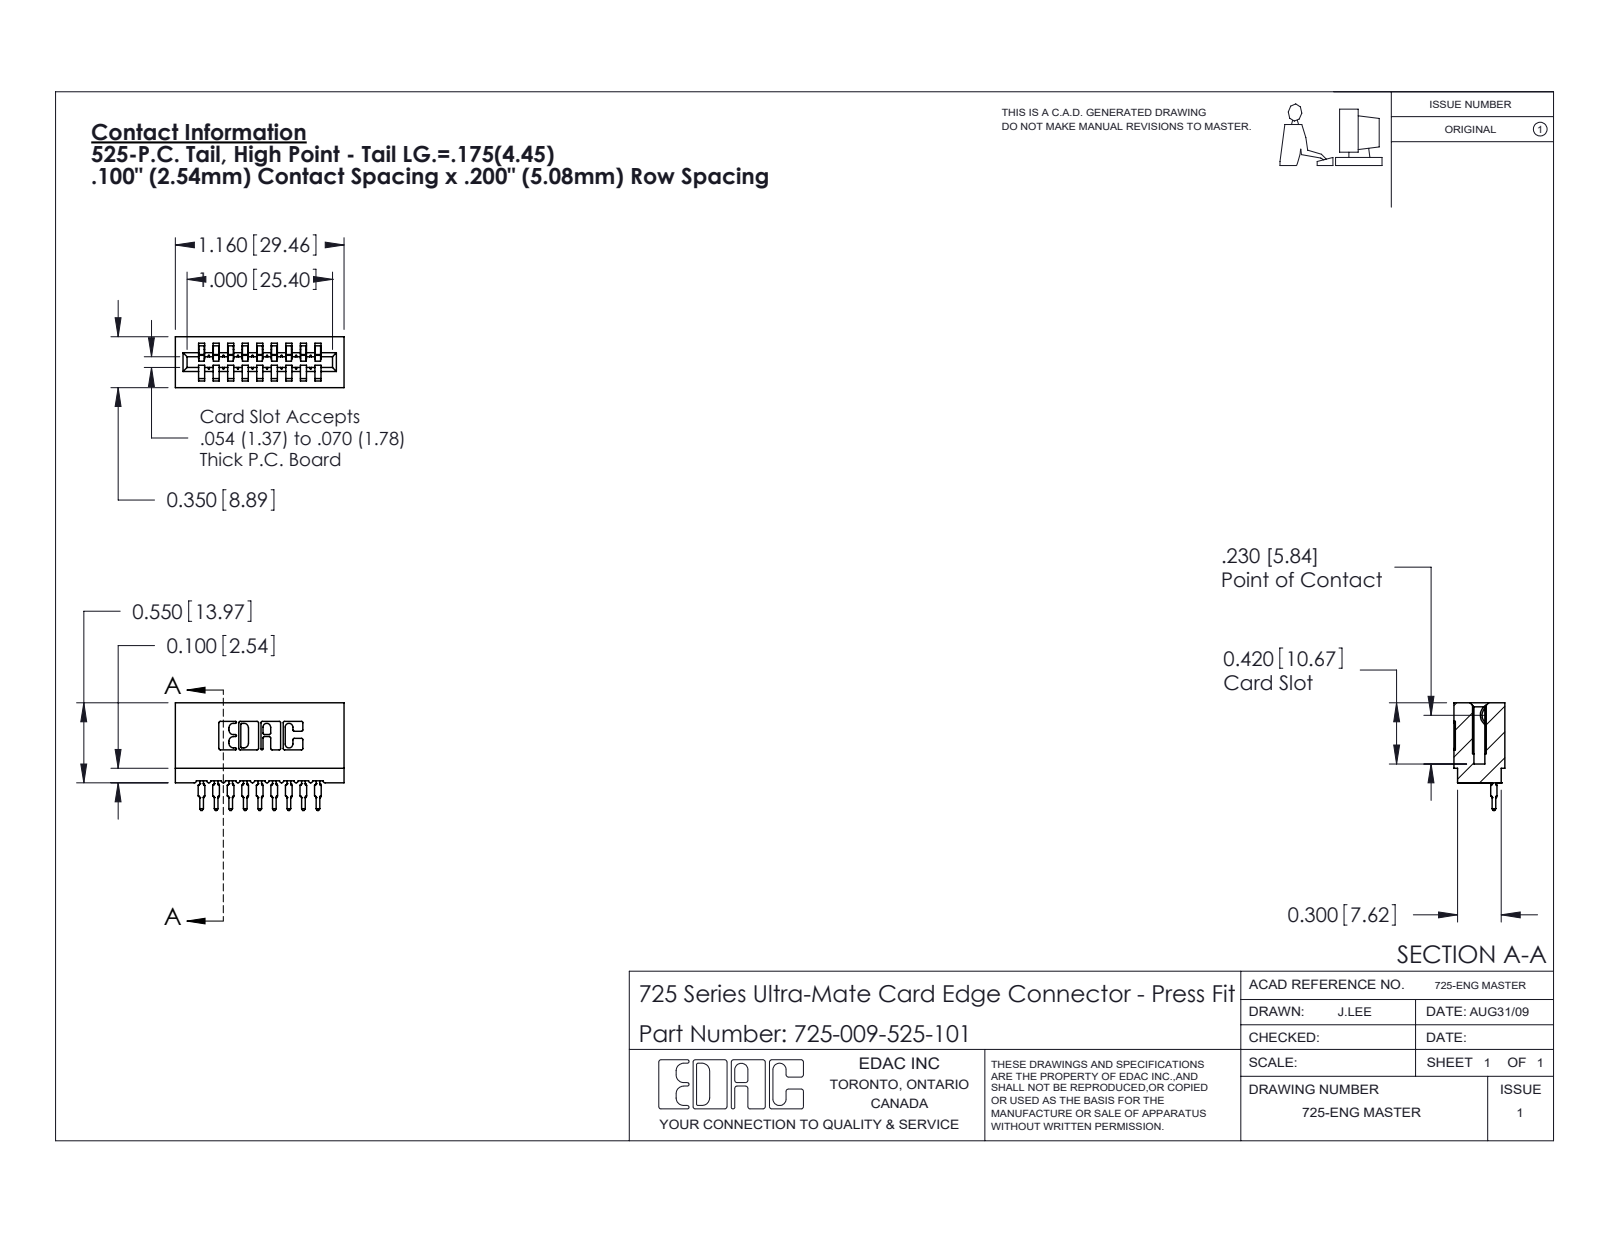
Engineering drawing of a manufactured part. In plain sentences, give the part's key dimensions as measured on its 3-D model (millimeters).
The part is named "745-292-001_525; 725-009-525-101; 725 Part_Insulator Option - 01". Its 3-D file was written by "SolidWorks 2020 (CONFIG_CONTROL_DESIGN)". It is 10 solids with 1103 faces: 658 planar, 211 cylindrical and 234 other. Overall it measures 29.5 by 18.8 by 8.9 millimeters. Its volume is 2 410 cubic millimeters and its surface area 4 028 square millimeters. Partial cylindrical surfaces (rounded edges, fillets, slot ends): 22 of radius 0.3, 18 of radius 0.4, 18 of radius 0.5, 6 of radius 0.2, 6 of radius 0.8, 4 of radius 0.1, 4 of radius 0.3, 3 of radius 0.7. The main face-to-face distances are 2.5, 5.1, 7.6, 10.2, 1.1, 12.7, 3.6, 1.5, 6.1, 4.
